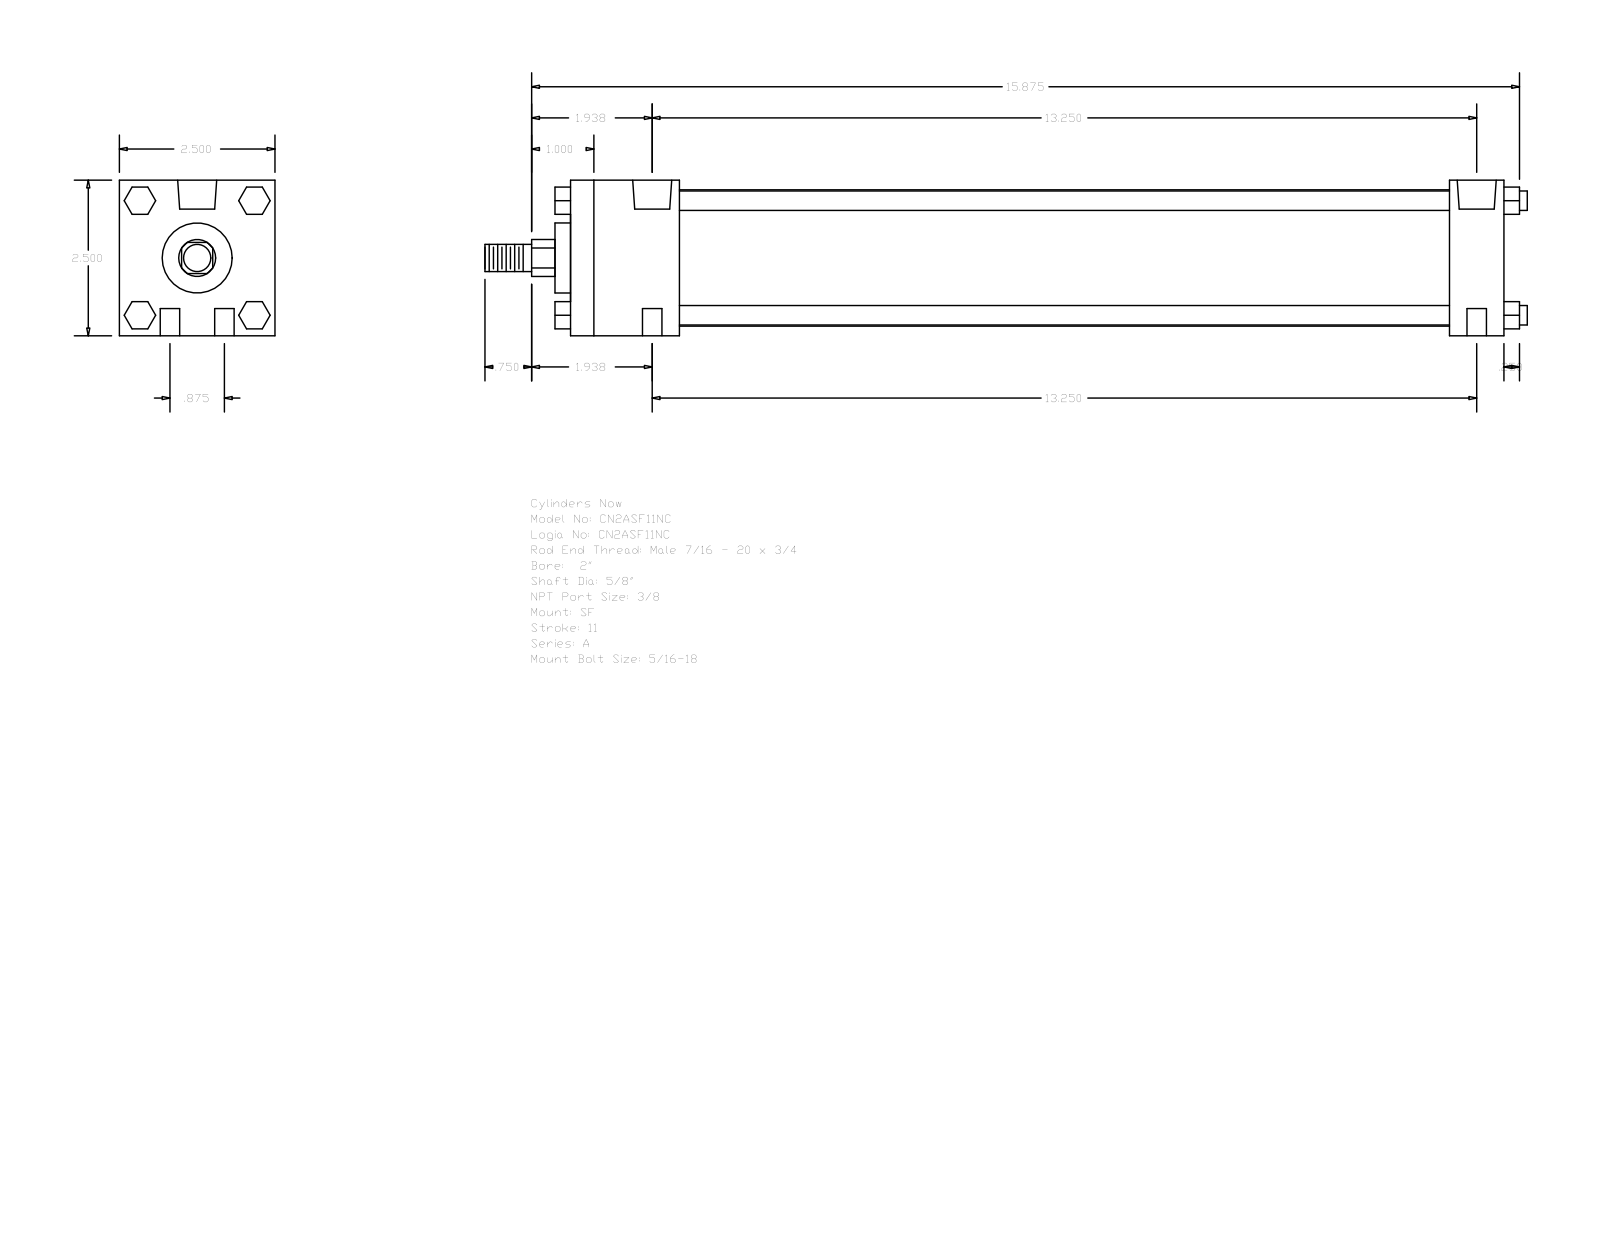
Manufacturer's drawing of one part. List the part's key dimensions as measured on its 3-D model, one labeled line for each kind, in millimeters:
Part name (STEP PRODUCT): A_SF__0200_0.625
STEP written by: GSSL Pune (CONFIG_CONTROL_DESIGN)
Units: millimetres
Bodies: 0 solids, 124 faces (94 planar, 30 cylindrical, 0 other)
Overall size (bounding box): 425.45 × 63.5 × 63.5
Round holes (diameter × count): ⌀7.94 ×4, ⌀5.56 ×2, ⌀15.93 ×2
Round bosses / shafts (diameter × count): ⌀7.94 ×4, ⌀55.63 ×1, ⌀28.57 ×1, ⌀15.88 ×1, ⌀11.11 ×1
Partial cylindrical surfaces — rounded edges, fillets, slot ends (radius × count): R7.54 ×1
Main face-to-face distances: 63.5, 381, 358.77, 22.23, 44.45, 314.32, 336.55, 6.35, 387.35, 50.8
Hole centre spacings: 11.11, 336.73, 336.55, 22.22, 337.28, 328.6
